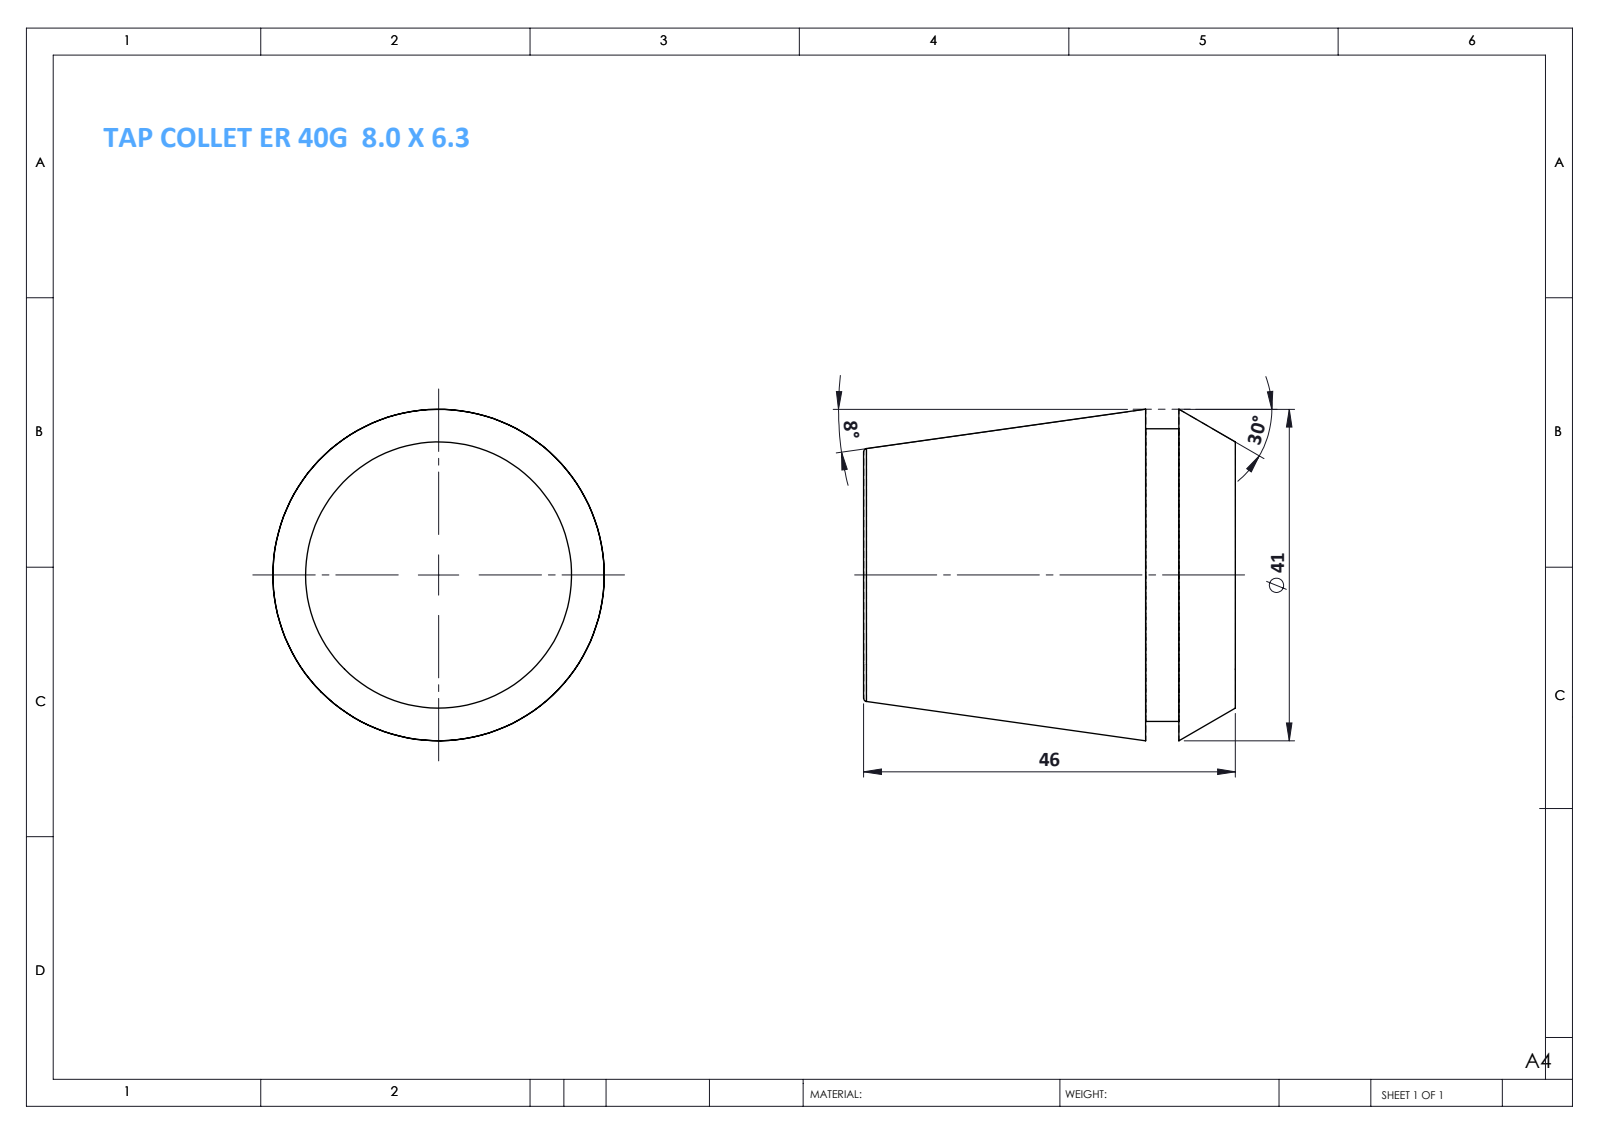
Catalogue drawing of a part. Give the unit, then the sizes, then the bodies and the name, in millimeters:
Units: millimetres
Overall size (bounding box): 46 × 41 × 41
Round bosses / shafts (diameter × count): ⌀36.2 ×1
Main face-to-face distances: 46, 11.1, 34.9, 7, 4.1, 39
Volume: 47 690 mm³ · Surface area: 7 586 mm²
Bodies: 1 solid, 12 faces (4 planar, 2 cylindrical, 6 other)
Part name (STEP PRODUCT): TAP COLLET ER 40G 8.0 X 6.3
STEP written by: SolidWorks 2014 (CONFIG_CONTROL_DESIGN)
